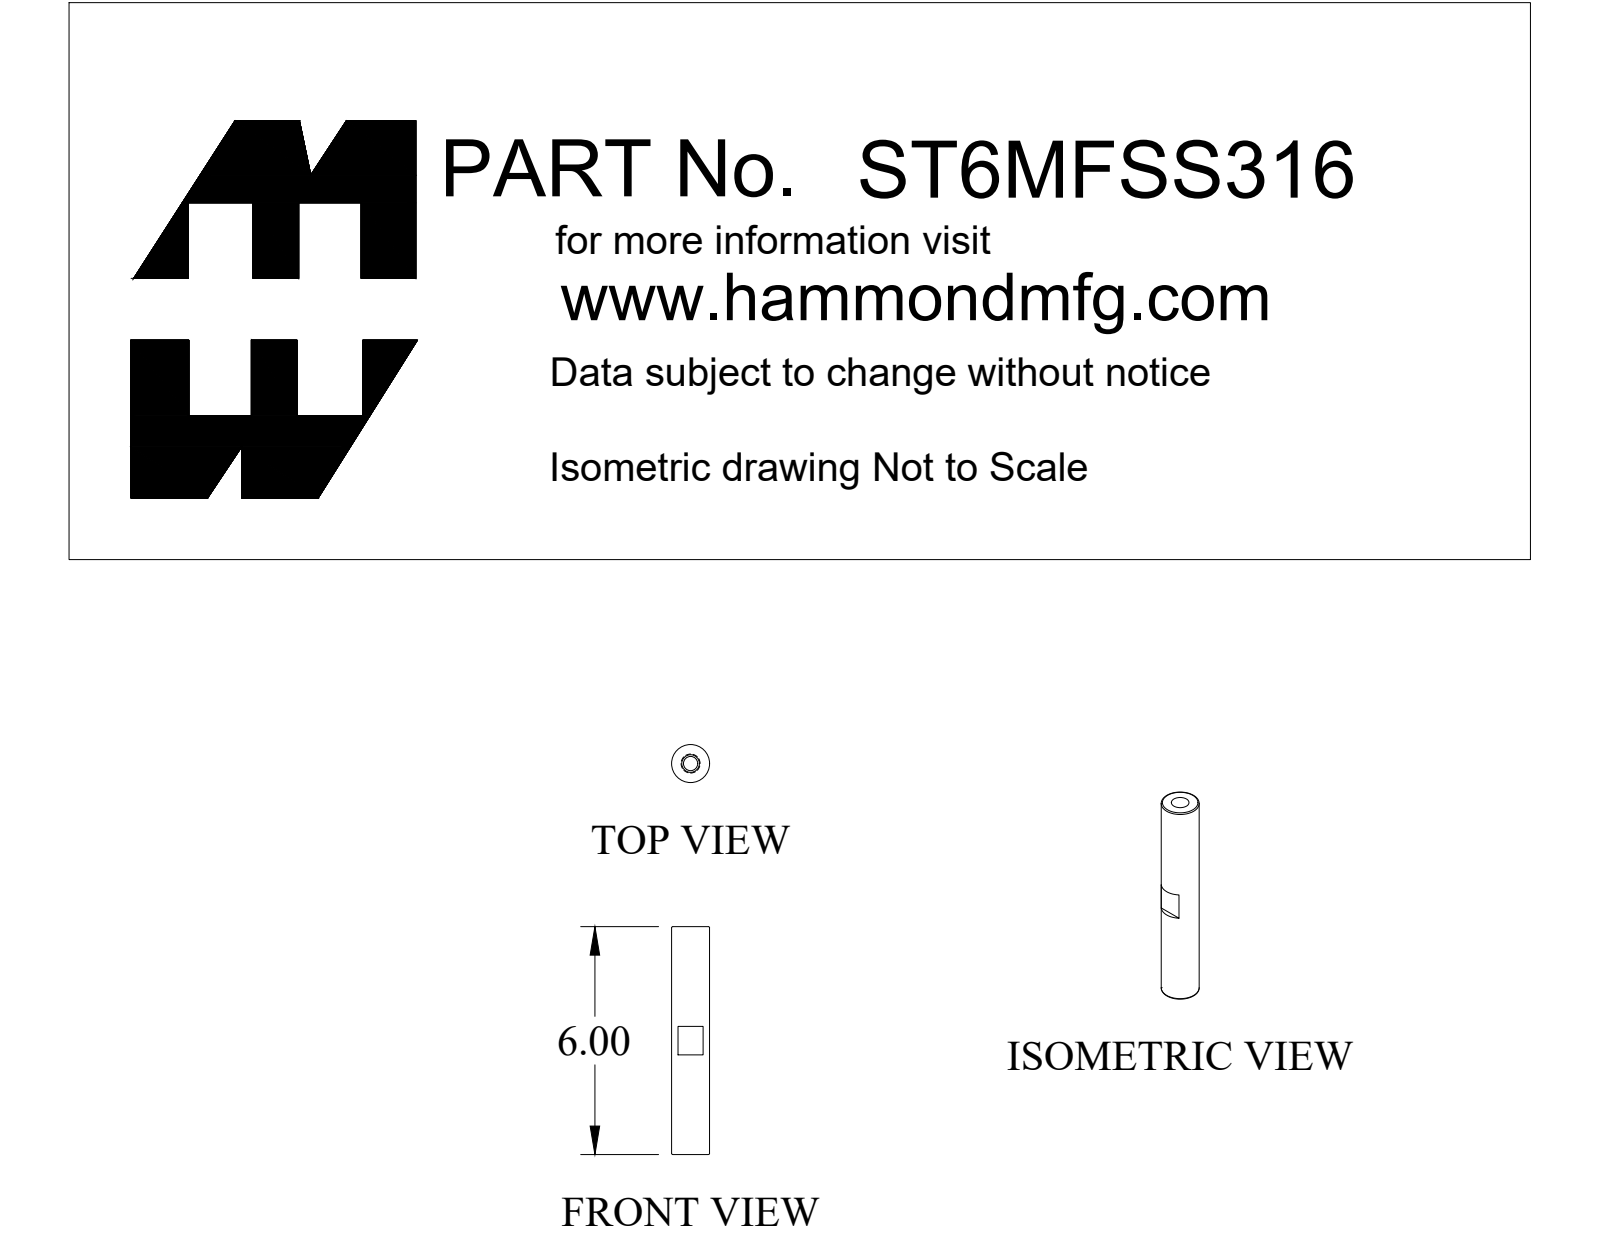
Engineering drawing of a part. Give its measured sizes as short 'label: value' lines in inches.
name: ST6MFSS316
written by: SolidWorks 2019 (CONFIG_CONTROL_DESIGN)
unit: in
bodies: 3 solids, 31 faces (21 planar, 7 cylindrical, 3 other)
size: 6.418 × 1 × 1
volume: 4.228 in³; area: 32.25 in²
holes: 1× ⌀0.375, 1× ⌀0.465, 1× ⌀0.532
bosses: 1× ⌀1, 1× ⌀0.5
face distances: 0.105, 0.75, 6, 6.105, 6.418, 0.418, 0.313, 0.75, 2.625, 3.375
